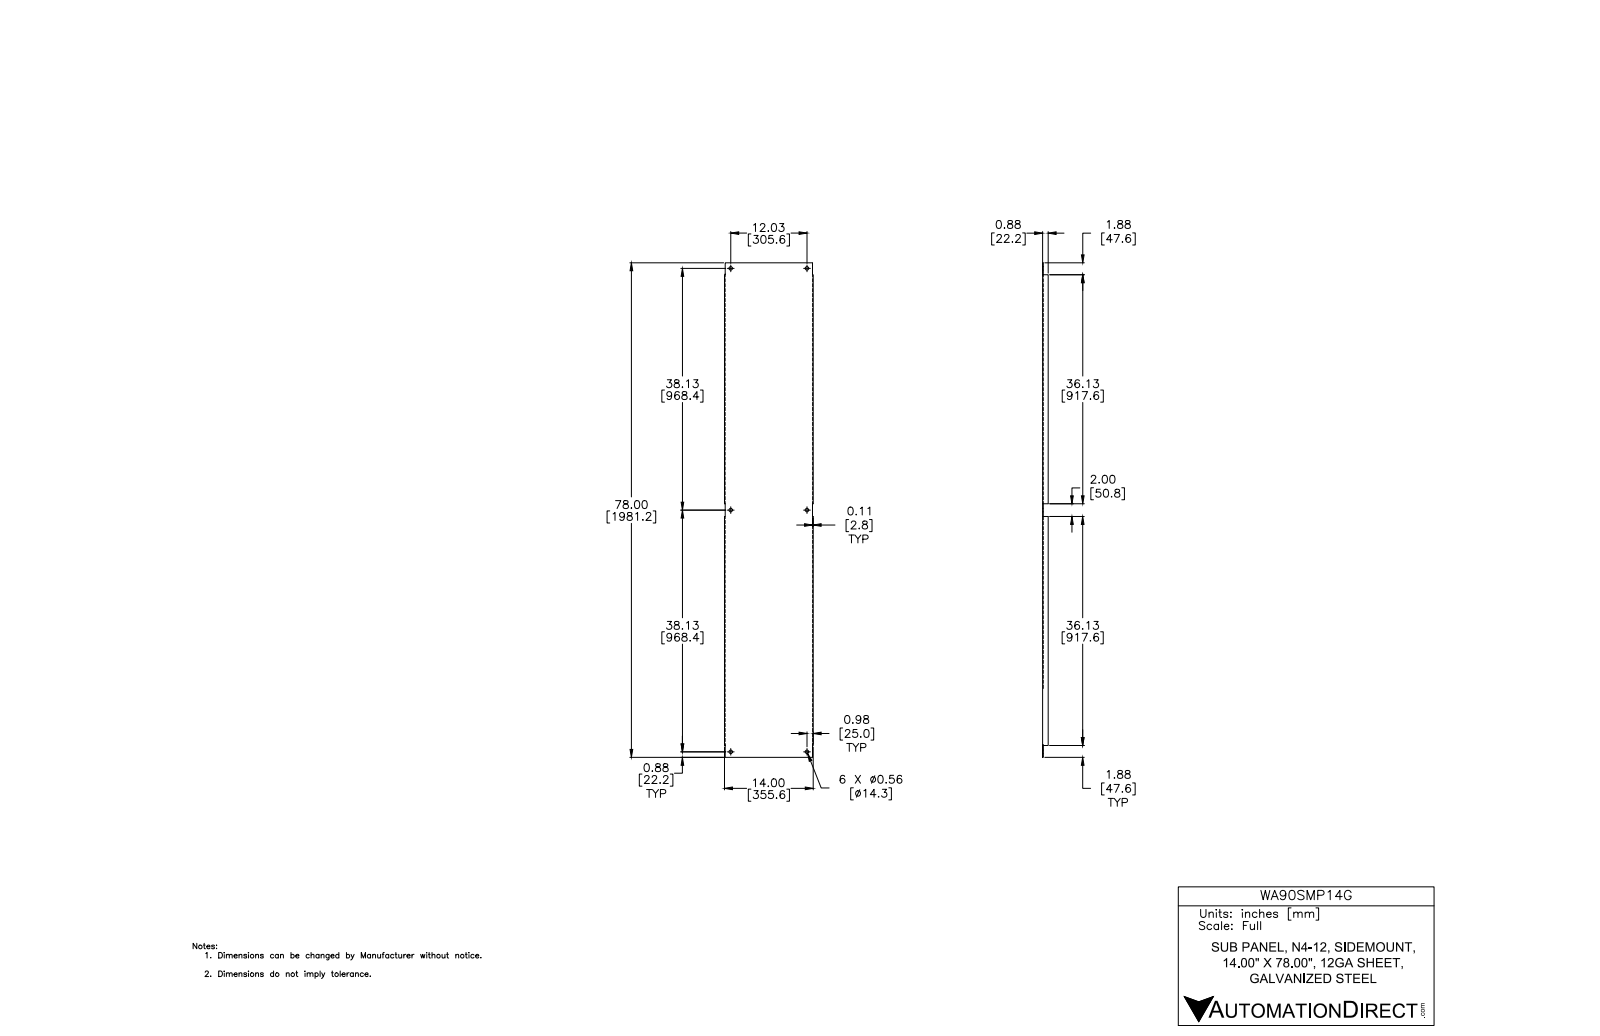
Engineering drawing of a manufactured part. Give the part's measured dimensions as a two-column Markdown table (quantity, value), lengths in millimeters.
| quantity | value |
| --- | --- |
| part name | WA60SMP14G-WA90SMP20G |
| STEP written by | Autodesk Inventor 2012 (AUTOMOTIVE_DESIGN) |
| units | millimeters |
| bodies | 1 solid, 48 faces (34 planar, 14 cylindrical, 0 other) |
| overall size | 1981.2 × 355.6 × 22.2 |
| volume | 1 840 000 mm³ |
| surface area | 1 558 000 mm² |
| round holes (diameter × count) | 14.3 × 6 |
| partial cylindrical surfaces (radius × count) | 0.4 × 2, 2.8 × 2 |
| main face-to-face distances | 2.4, 353.2, 350.9, 355.6, 19.8, 22.2, 1981.2, 2.8, 352.8, 0.4 |
| hole center spacings | 968.4, 1015.5, 305.6, 1936.8, 1960.7 |
